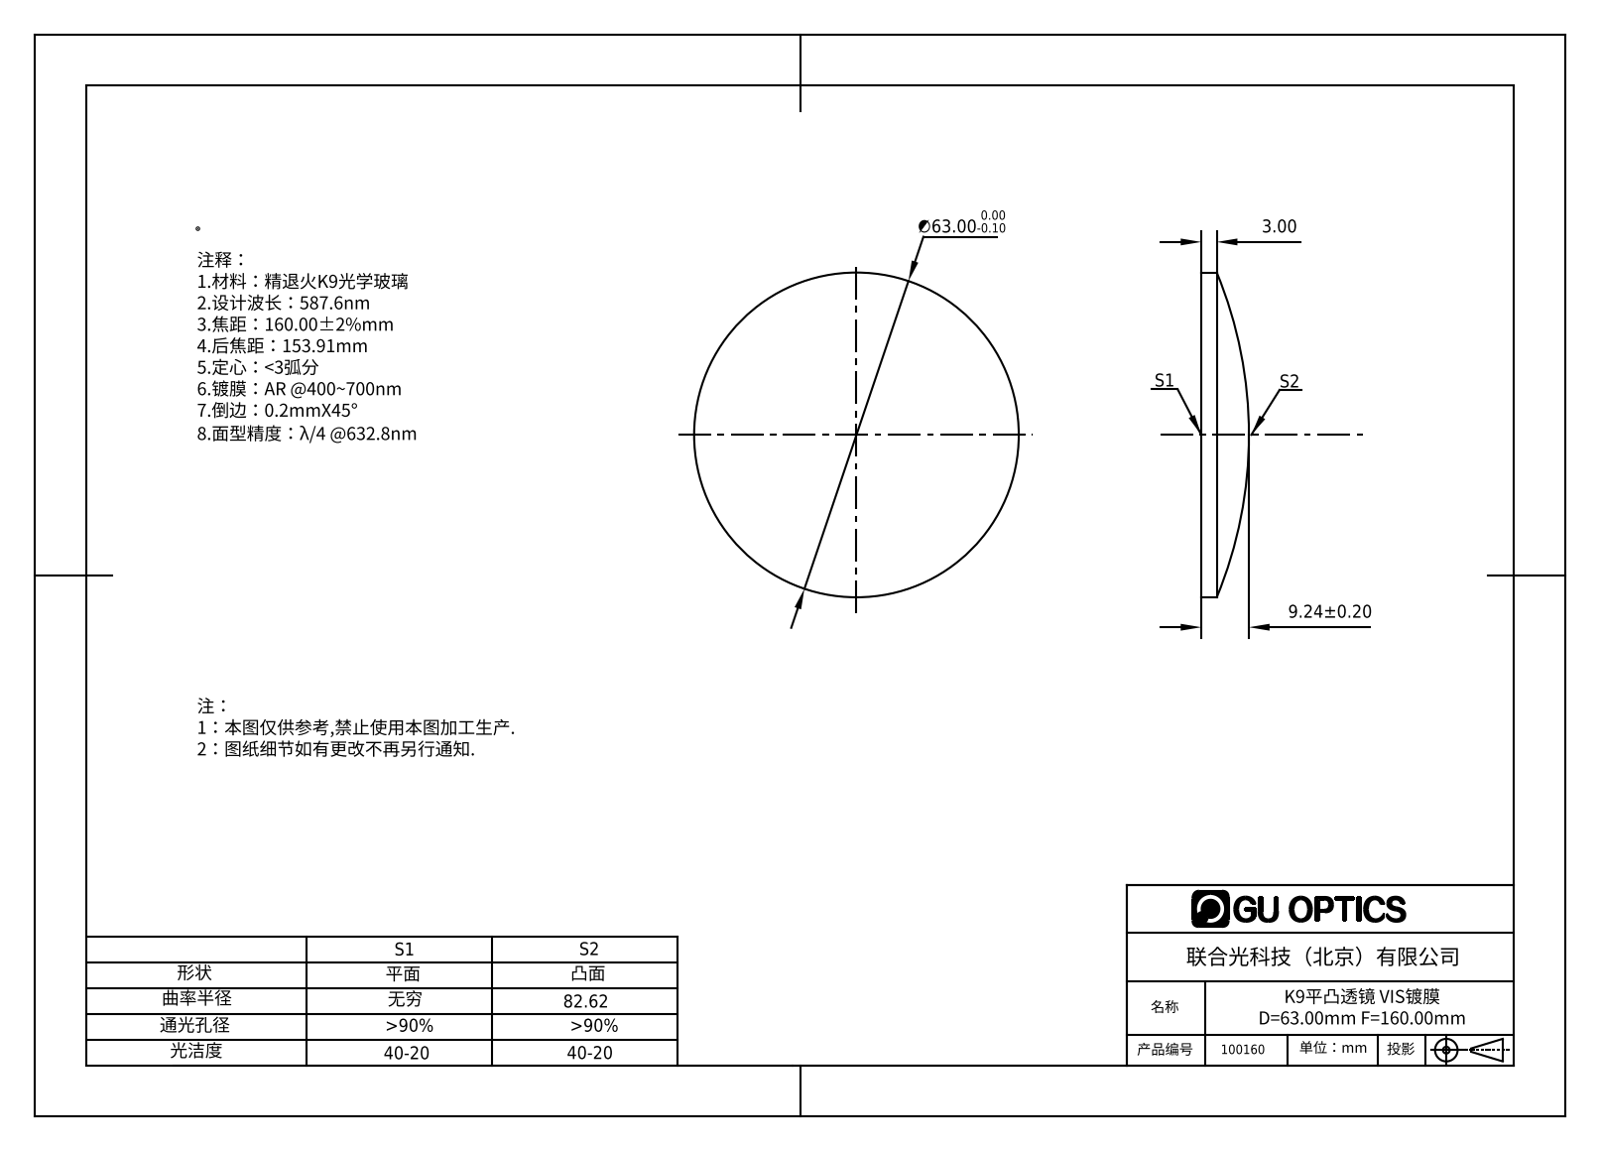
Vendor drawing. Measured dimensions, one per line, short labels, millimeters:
name: 100160
written by: SolidWorks 2016 (AUTOMOTIVE_DESIGN)
unit: mm
bodies: 1 solid, 5 faces (1 planar, 2 cylindrical, 2 other)
size: 63 × 63 × 9.24
volume: 19 205 mm³; area: 6 951 mm²
bosses: 1× ⌀63
